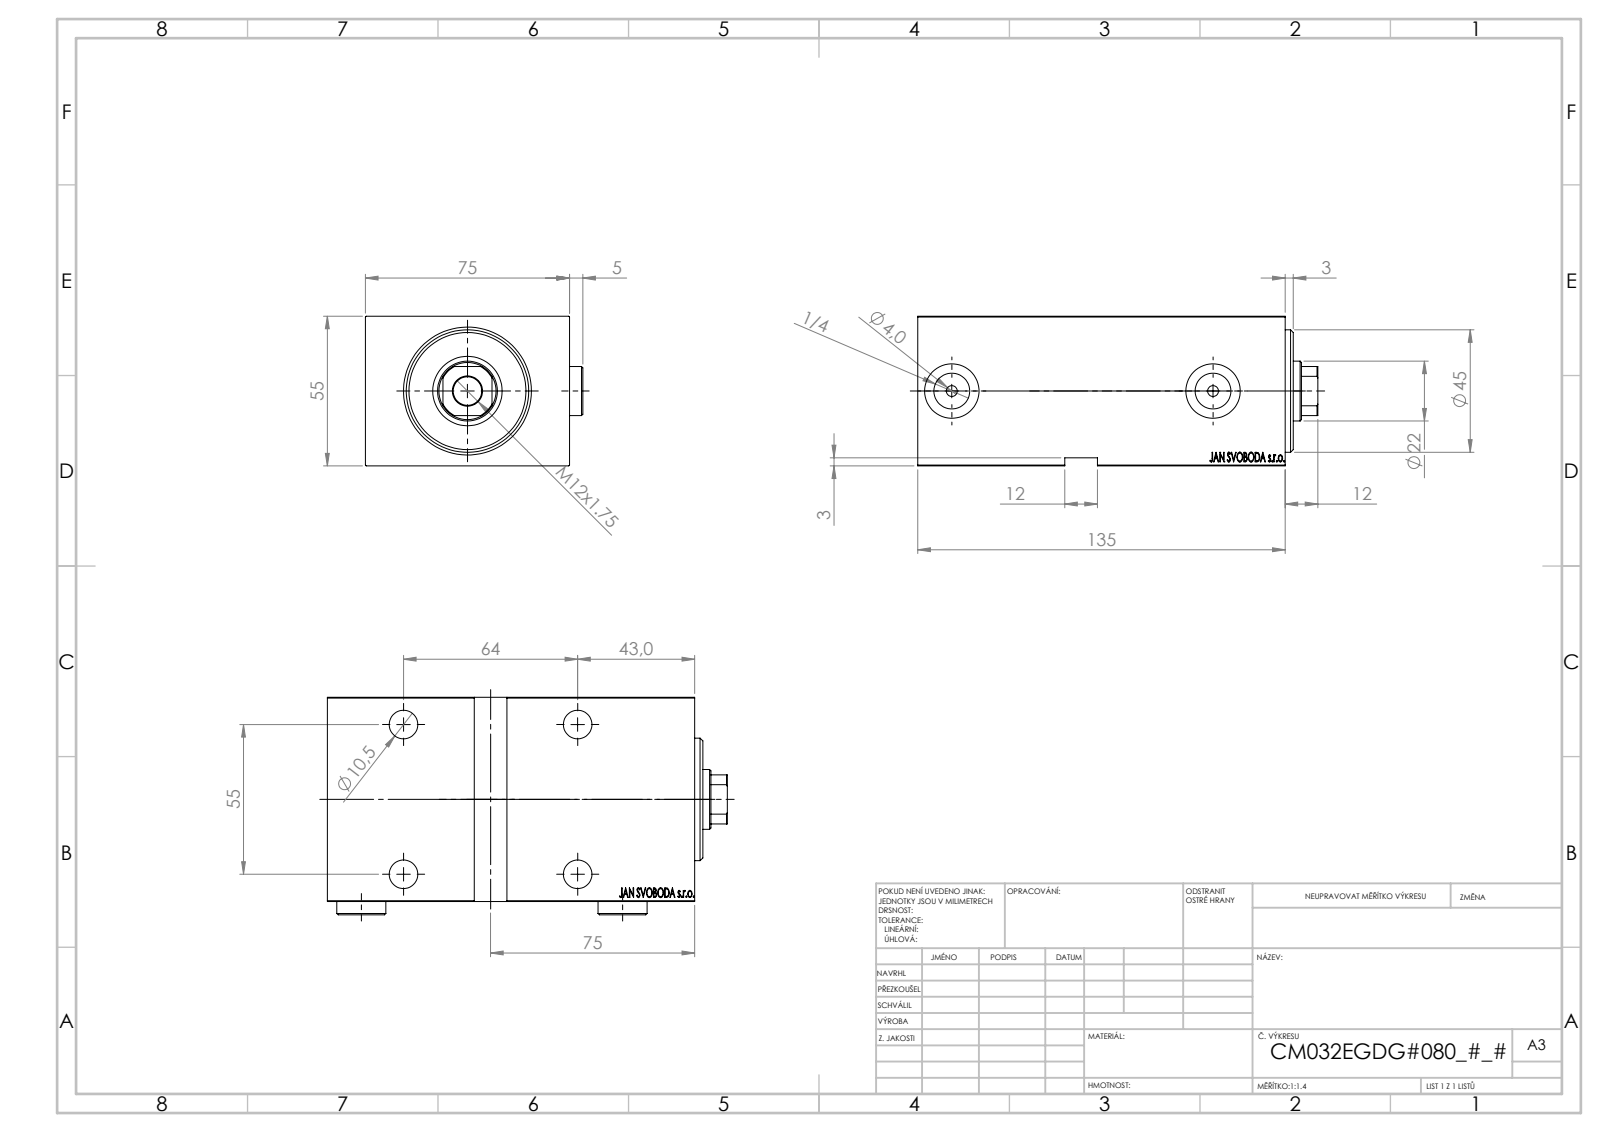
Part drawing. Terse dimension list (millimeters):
name: V450CM_VC_B; Zatka_OIL_PORT; V450CM_E_Body; V450CM_E_VCP
written by: SolidWorks 2019 (CONFIG_CONTROL_DESIGN)
unit: mm
bodies: 5 solids, 909 faces (445 planar, 66 cylindrical, 398 other)
size: 147 × 79.9 × 55
volume: 496 699 mm³; area: 87 145 mm²
holes: 5× ⌀10.5, 4× ⌀16.5, 2× ⌀4, 2× ⌀13.16, 2× ⌀20, 1× ⌀22, 1× ⌀25.5, 1× ⌀32, 1× ⌀45
bosses: 2× ⌀18, 1× ⌀34
rounds: 1× R10.5
face distances: 55, 75, 135, 3, 5, 10, 125, 130, 120, 74.9
hole spacings: 55, 64, 84.39, 96
